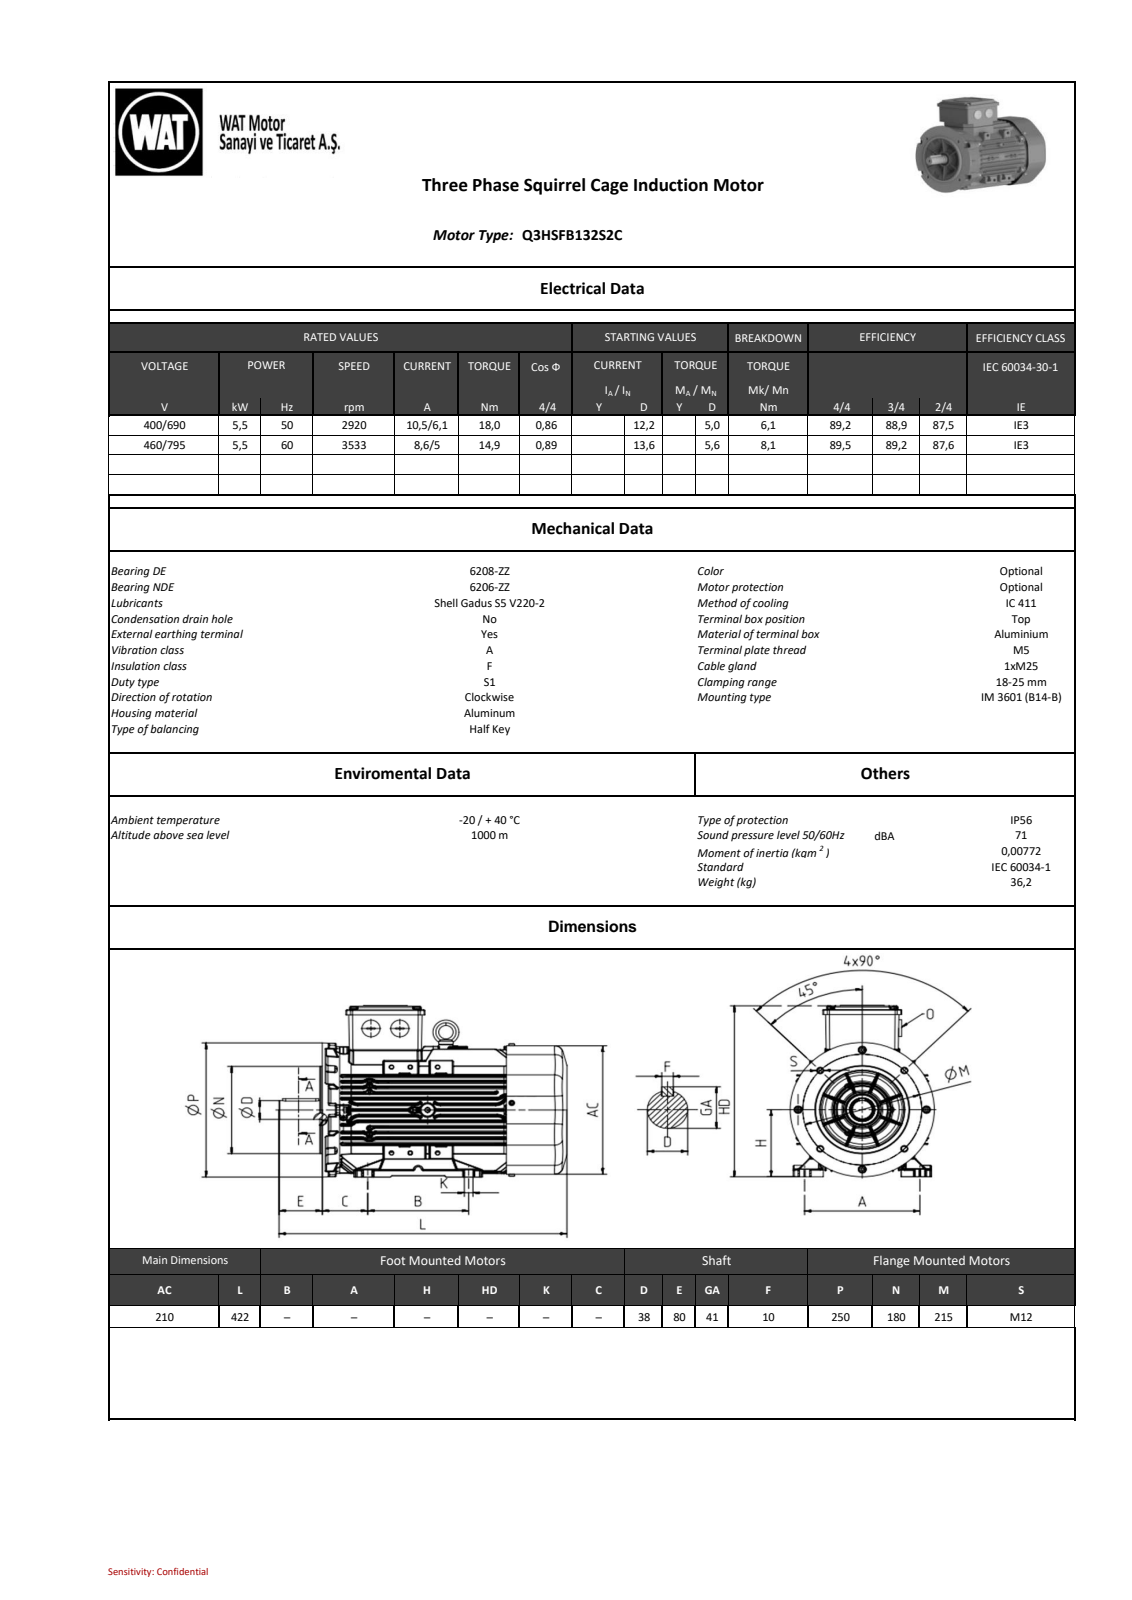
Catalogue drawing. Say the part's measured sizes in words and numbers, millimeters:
The part is named "Ar311510F80553vw". Its 3-D file was written by "SIEMENS PLM Software NX 9.0 (AUTOMOTIVE_DESIGN)". It is 0 solids with 7816 faces: 1522 planar, 2432 cylindrical and 3862 other. Overall it measures 422 by 276.25 by 250.56 millimeters. Round holes: 6 of diameter 12, 5 of diameter 10.3, 2 of diameter 27.8, 1 of diameter 4, 1 of diameter 4.72, 1 of diameter 8, 1 of diameter 13, 1 of diameter 57.4, 1 of diameter 58.67, 1 of diameter 241. Round bosses or shafts: 8 of diameter 8, 4 of diameter 20, 4 of diameter 11.8, 4 of diameter 10, 4 of diameter 6, 1 of diameter 188, 1 of diameter 187.3, 1 of diameter 180. Partial cylindrical surfaces (rounded edges, fillets, slot ends): 749 of radius 0.5, 502 of radius 0.8, 192 of radius 1, 140 of radius 2, 37 of radius 3, 16 of radius 0.38, 8 of radius 4, 7 of radius 0.75. The main face-to-face distances are 1, 10.99, 35.96, 32.44, 88.6, 21.5, 24.97, 9.67, 111.37, 22.45. The hole center spacings are 40, 107.49, 107.5, 152.02, 152.03, 215.
